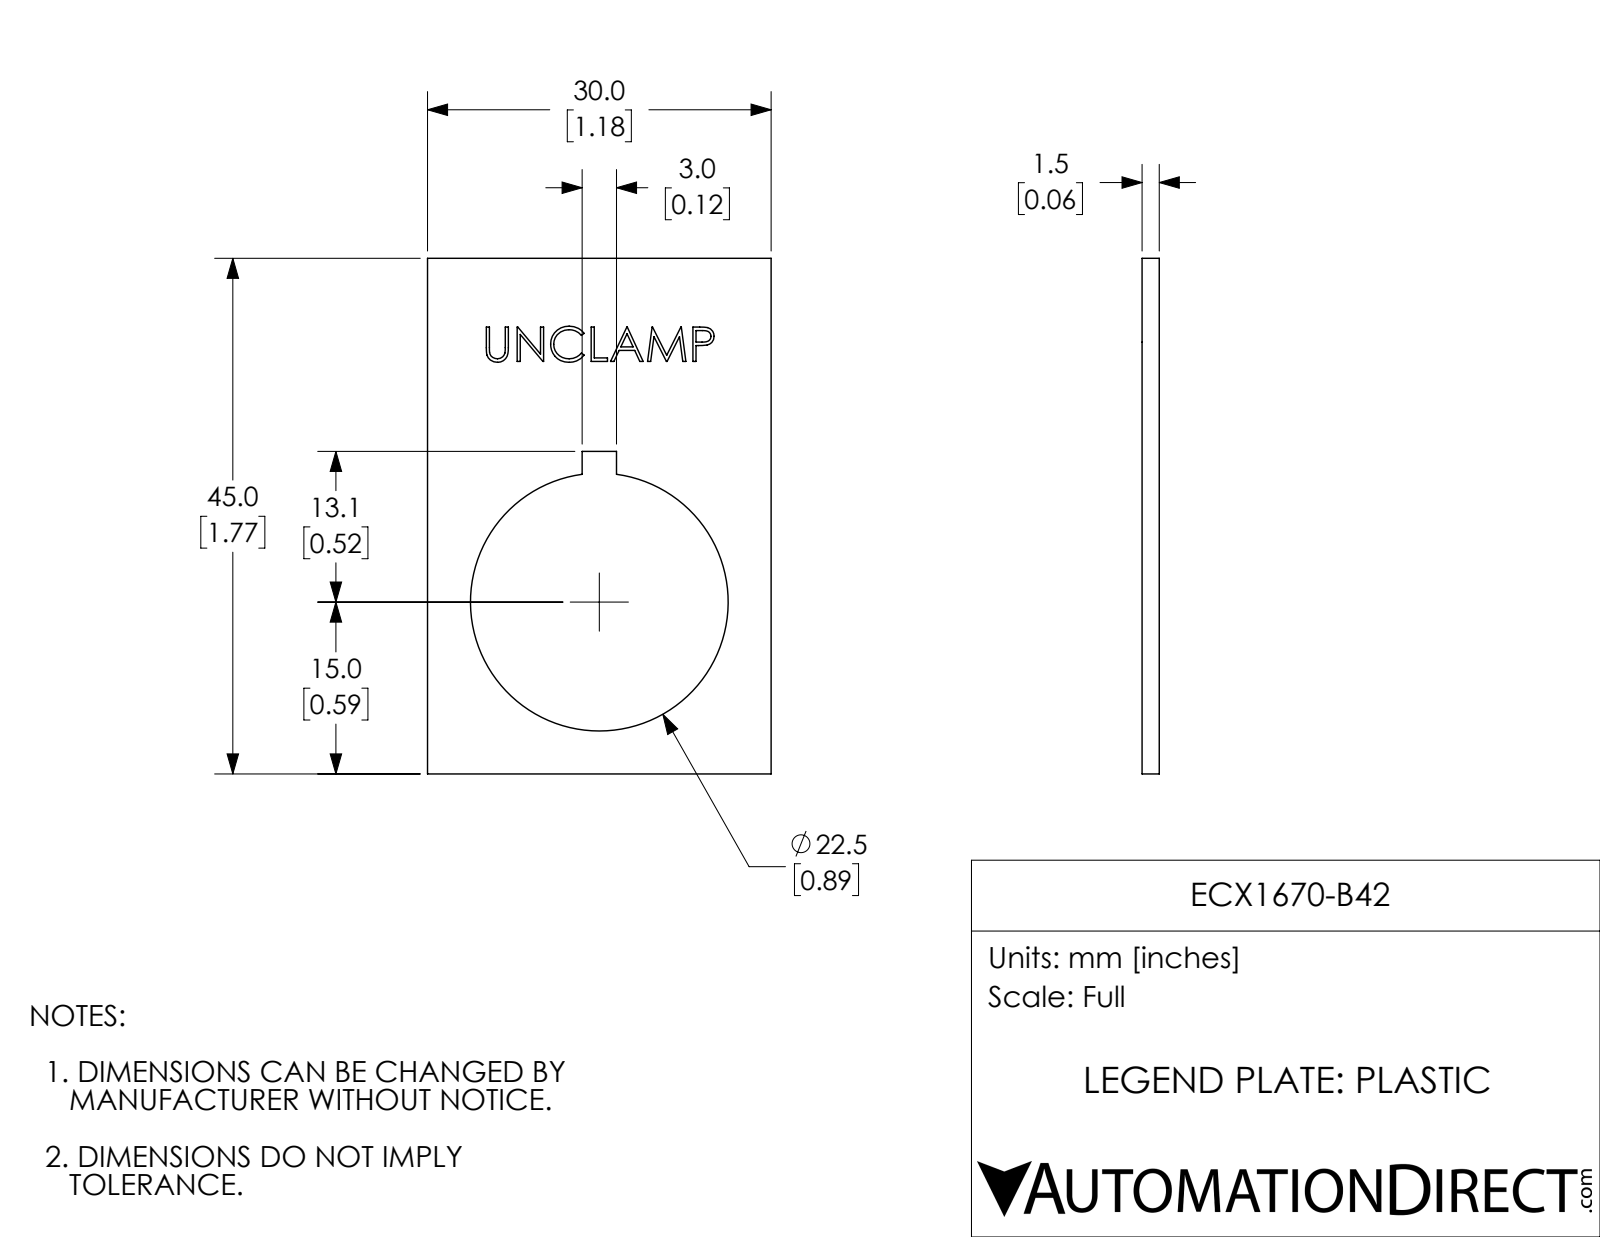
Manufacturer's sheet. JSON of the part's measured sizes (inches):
{"part_name": "ECX1670-B42", "step_written_by": "SolidWorks 2017 (AUTOMOTIVE_DESIGN)", "units": "inches", "bodies": {"solids": 1, "faces": 99, "planar": 74, "cylindrical": 3, "other": 22}, "overall_size": [1.772, 1.181, 0.059], "volume_in3": 0.087, "surface_area_in2": 3.461, "round_holes": [[0.886, 1]], "face_to_face_distances": [0.059, 1.181, 1.772, 0.058, 0.531, 0.65, 1.108, 0.663, 0.118, 0.35]}
